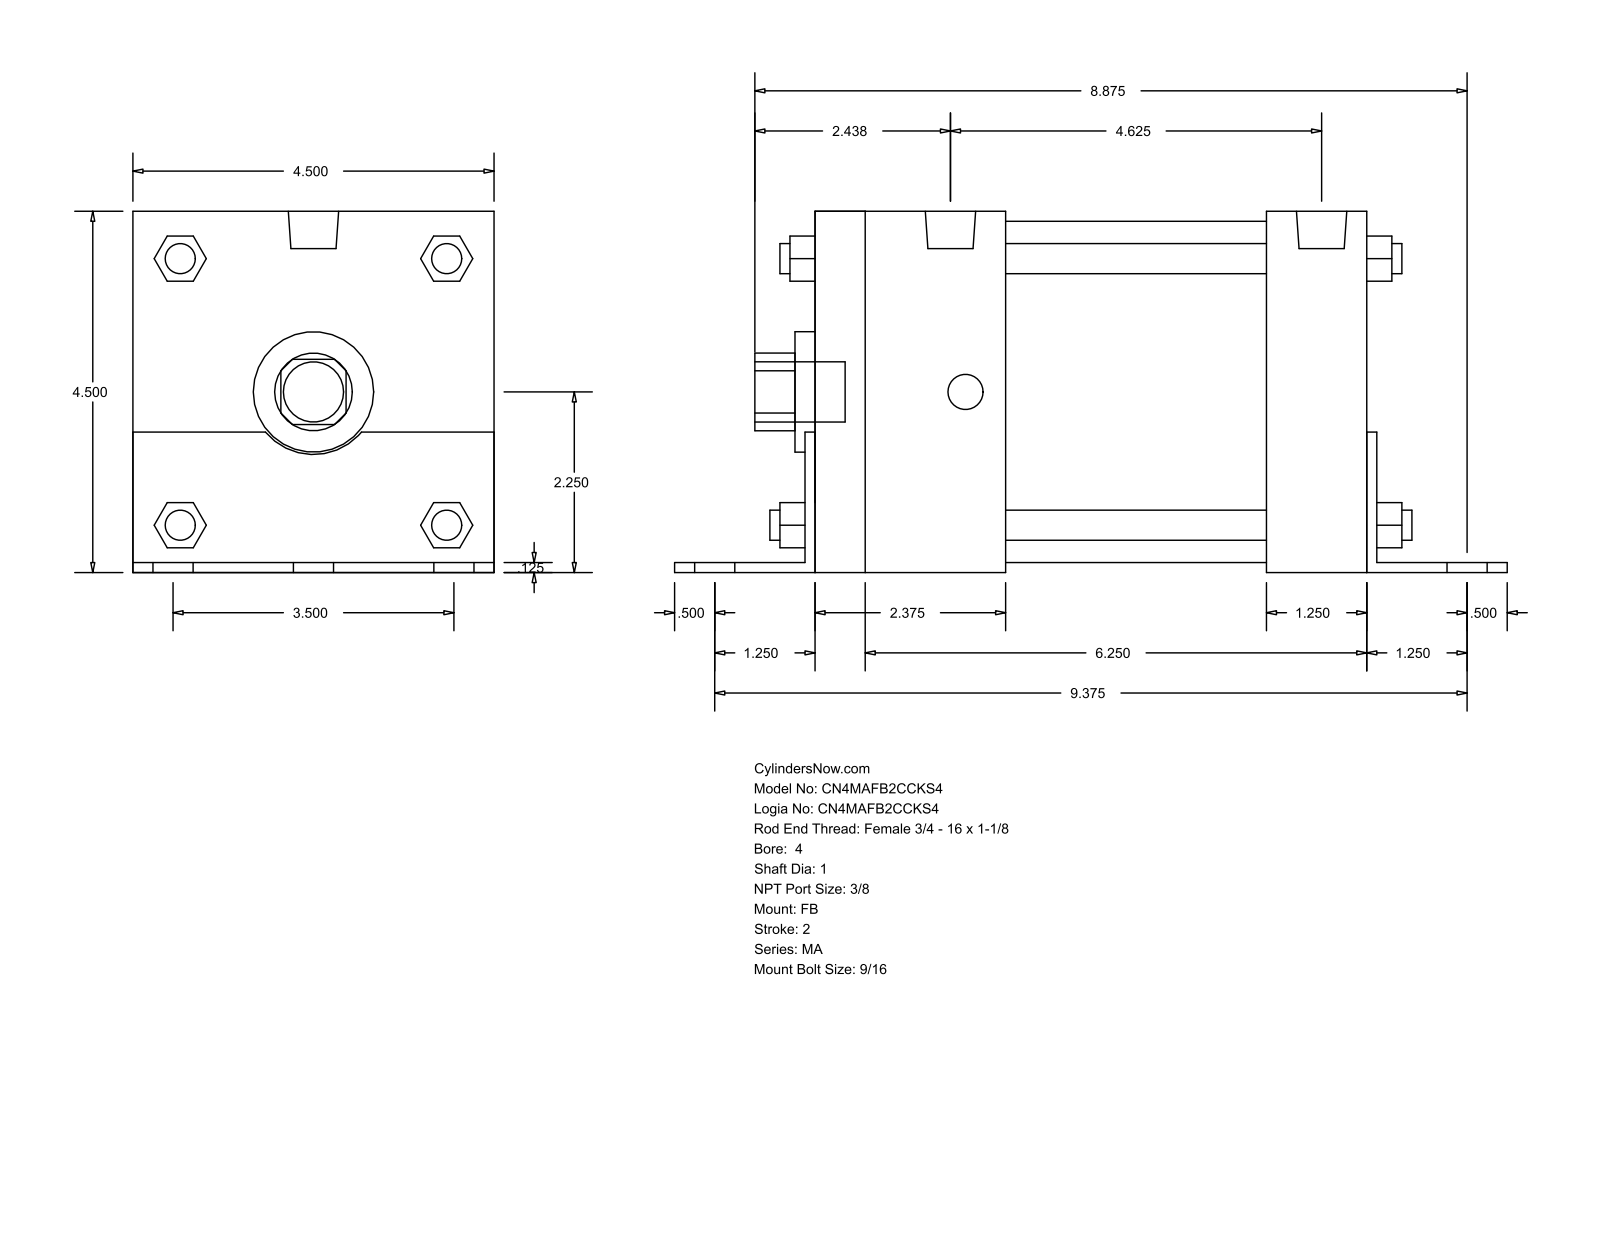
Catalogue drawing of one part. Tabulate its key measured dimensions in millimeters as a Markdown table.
| quantity | value |
| --- | --- |
| part name | MA_FB__0400_1 |
| STEP written by | GSSL Pune (CONFIG_CONTROL_DESIGN) |
| units | millimeters |
| bodies | 0 solids, 140 faces (105 planar, 35 cylindrical, 0 other) |
| overall size | 263.52 × 114.35 × 114.3 |
| round holes (diameter × count) | 25.4 × 1, 38.1 × 1, 107.95 × 1 |
| round bosses / shafts (diameter × count) | 14.29 × 6, 11.11 × 4, 9.53 × 4, 15.93 × 2, 19.05 × 1 |
| partial cylindrical surfaces (radius × count) | 12.29 × 1, 19.81 × 1 |
| main face-to-face distances | 114.3, 3.17, 114.35, 177.8, 3.12, 111.18, 174.63, 180.97, 146.05, 142.88 |
